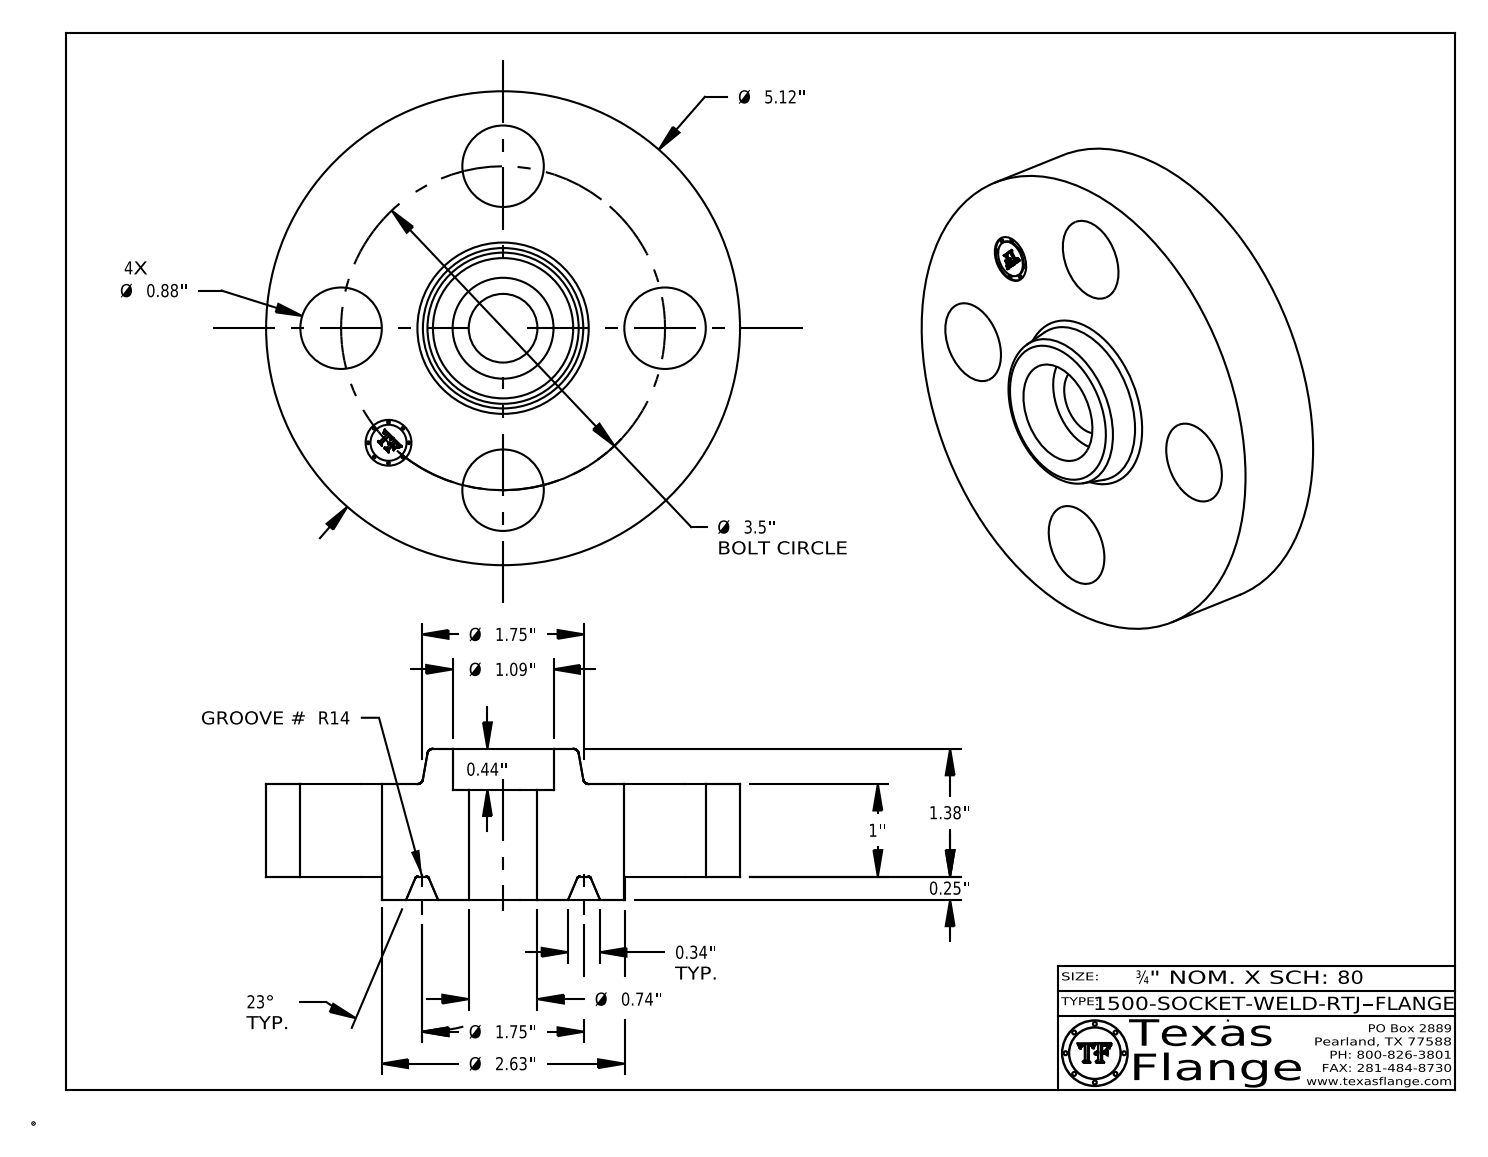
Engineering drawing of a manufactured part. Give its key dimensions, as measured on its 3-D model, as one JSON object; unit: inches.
{"part_name": "1500-SOCKET-WELD-RTJ", "step_written_by": "CATIA V5 STEP AP214 (AUTOMOTIVE_DESIGN)", "units": "inches", "bodies": {"solids": 1, "faces": 426, "planar": 372, "cylindrical": 40, "other": 14}, "overall_size": [5.12, 5.12, 1.63], "volume_in3": 19.1, "surface_area_in2": 72.3, "round_holes": [[0.88, 4], [0.495, 1], [0.742, 1], [1.09, 1]], "round_bosses_or_shafts": [[0.03, 8], [5.12, 1], [2.625, 1], [0.39, 1]], "face_to_face_distances": [1, 0.25, 1.25, 1.63, 1.38, 0.38, 0.06, 1.19, 0.94, 0.44], "hole_center_spacings": [1.75, 2.475, 1.339, 3.233, 3.5]}
